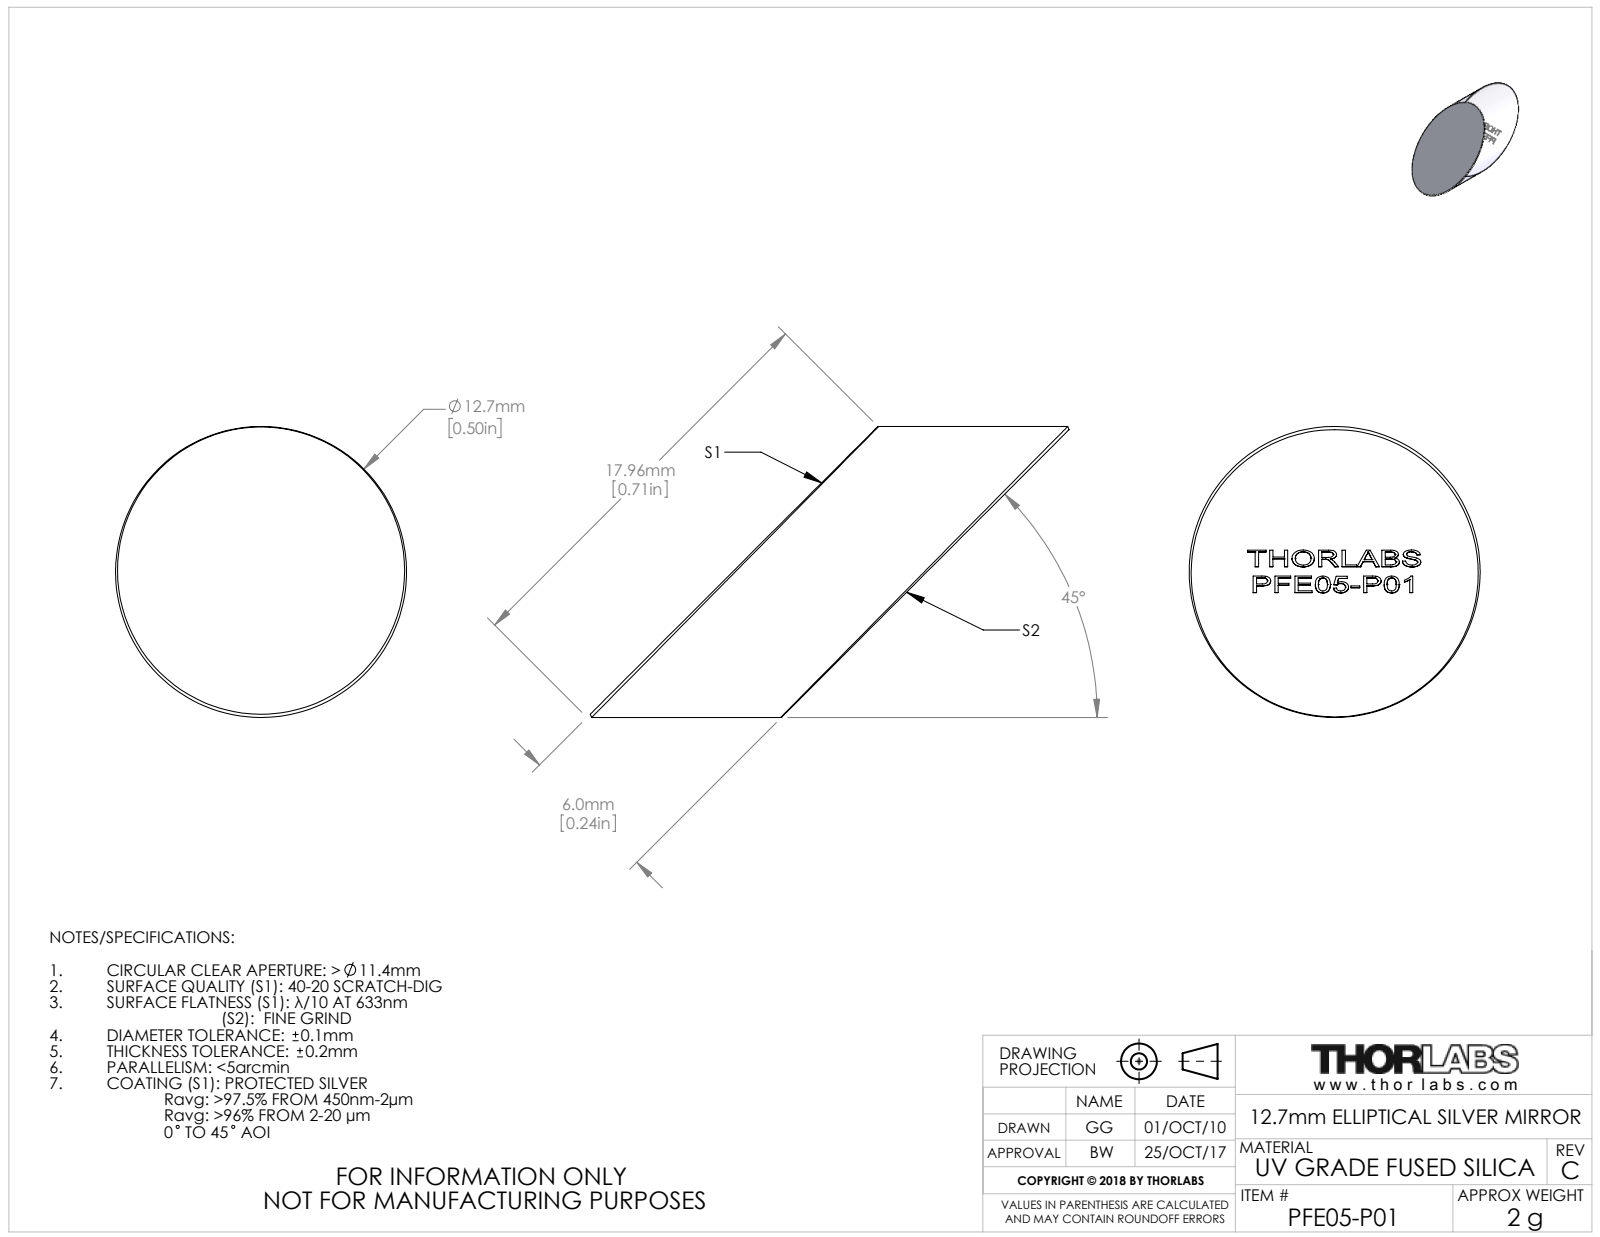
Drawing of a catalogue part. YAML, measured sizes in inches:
part_name: "21548-E0W"
step_written_by: "SolidWorks 2016 (CONFIG_CONTROL_DESIGN)"
units: inches
bodies: {solids: 1, faces: 232, planar: 141, cylindrical: 2, other: 89}
overall_size: [0.823, 0.5, 0.5]
volume: 0.066
surface_area: 1.068
round_bosses_or_shafts:
  - {diameter: 0.5, count: 1}
face_to_face_distances: [0.236, 0.063, 0.041, 0.028, 0.036, 0.017, 0.022, 0.031, 0.019, 0.034]
